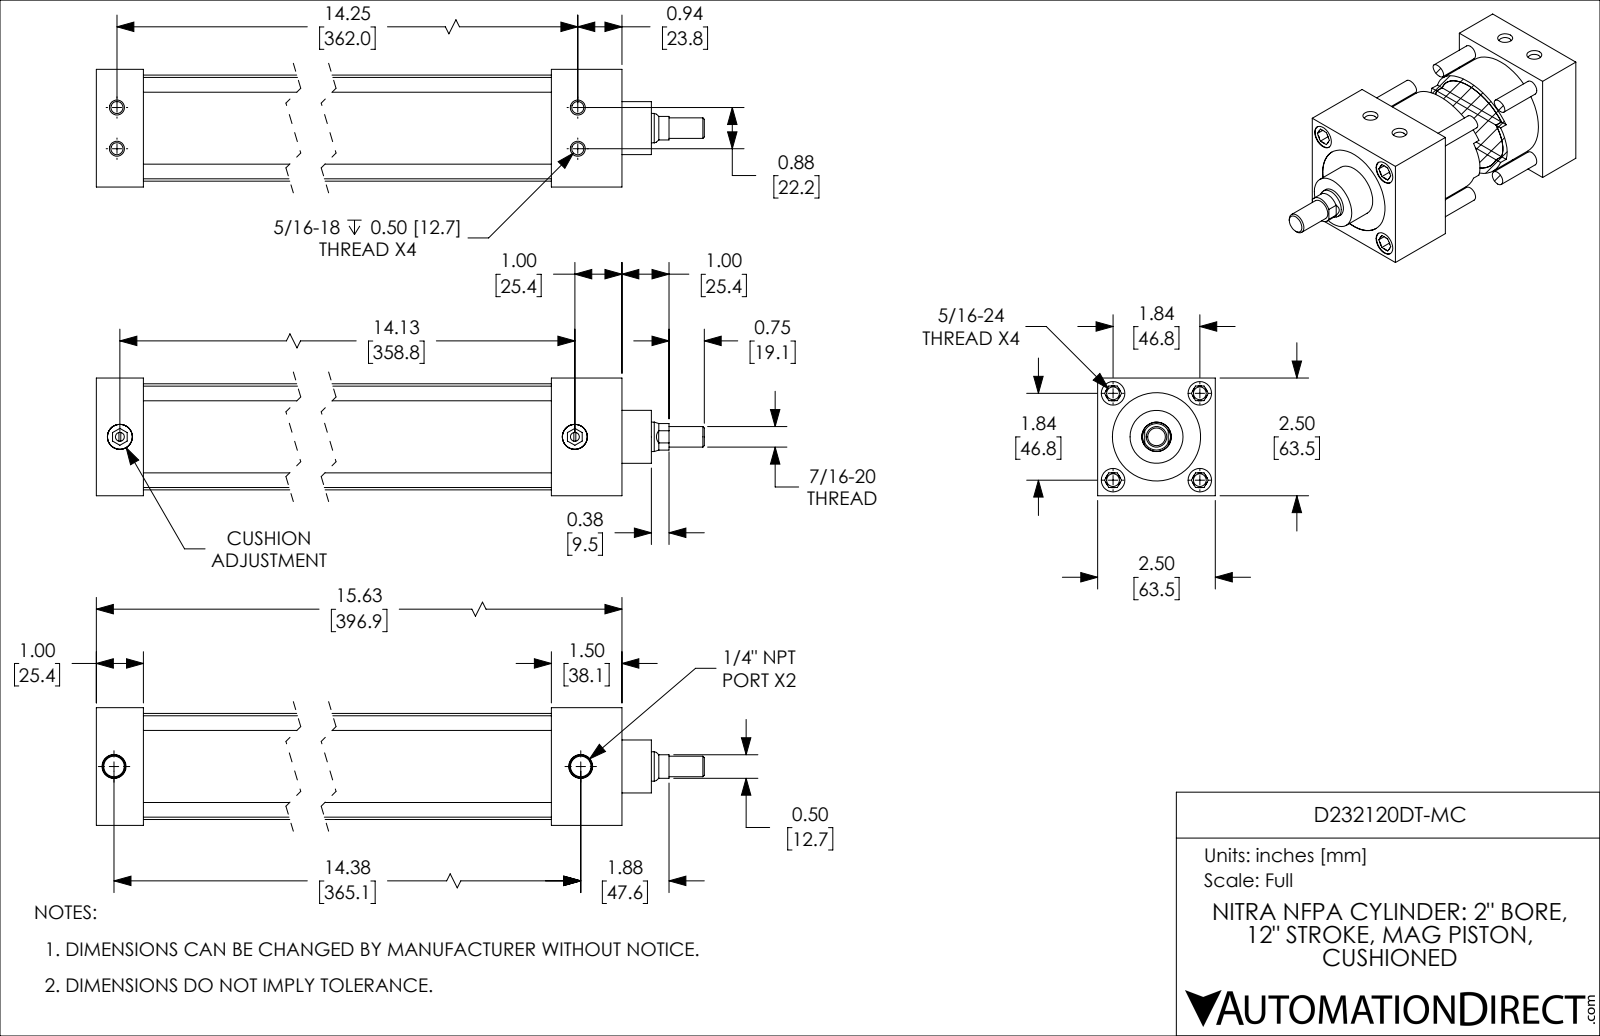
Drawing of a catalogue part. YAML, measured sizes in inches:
part_name: "D232120DT-MC_BODY; D232120DT-MC_CUSHION; D232120DT-MC_PISTON_KK1; D232120DT-MC"
step_written_by: "SolidWorks 2019 (CONFIG_CONTROL_DESIGN)"
units: inches
bodies: {solids: 4, faces: 248, planar: 90, cylindrical: 78, other: 80}
overall_size: [17.375, 2.5, 2.5]
volume: 37.78
surface_area: 334.8
round_holes:
  - {diameter: 0.272, count: 7}
  - {diameter: 0.257, count: 4}
  - {diameter: 0.5, count: 4}
  - {diameter: 0.19, count: 2}
  - {diameter: 0.438, count: 2}
  - {diameter: 0.531, count: 2}
  - {diameter: 0.626, count: 1}
  - {diameter: 1.875, count: 1}
  - {diameter: 2.001, count: 1}
round_bosses_or_shafts:
  - {diameter: 0.312, count: 4}
  - {diameter: 0.532, count: 2}
  - {diameter: 2.251, count: 1}
  - {diameter: 1.999, count: 1}
  - {diameter: 1.125, count: 1}
  - {diameter: 0.624, count: 1}
  - {diameter: 0.437, count: 1}
partial_cylinders:
  - {radius: 0.281, count: 1}
face_to_face_distances: [2.5, 1, 14.125, 13.125, 1.125, 2.125, 12, 15.625, 14.625, 13.5]
hole_center_spacings: [1.84, 1.844, 1.301, 0.441, 0.443, 0.875, 1.304, 2.602]
